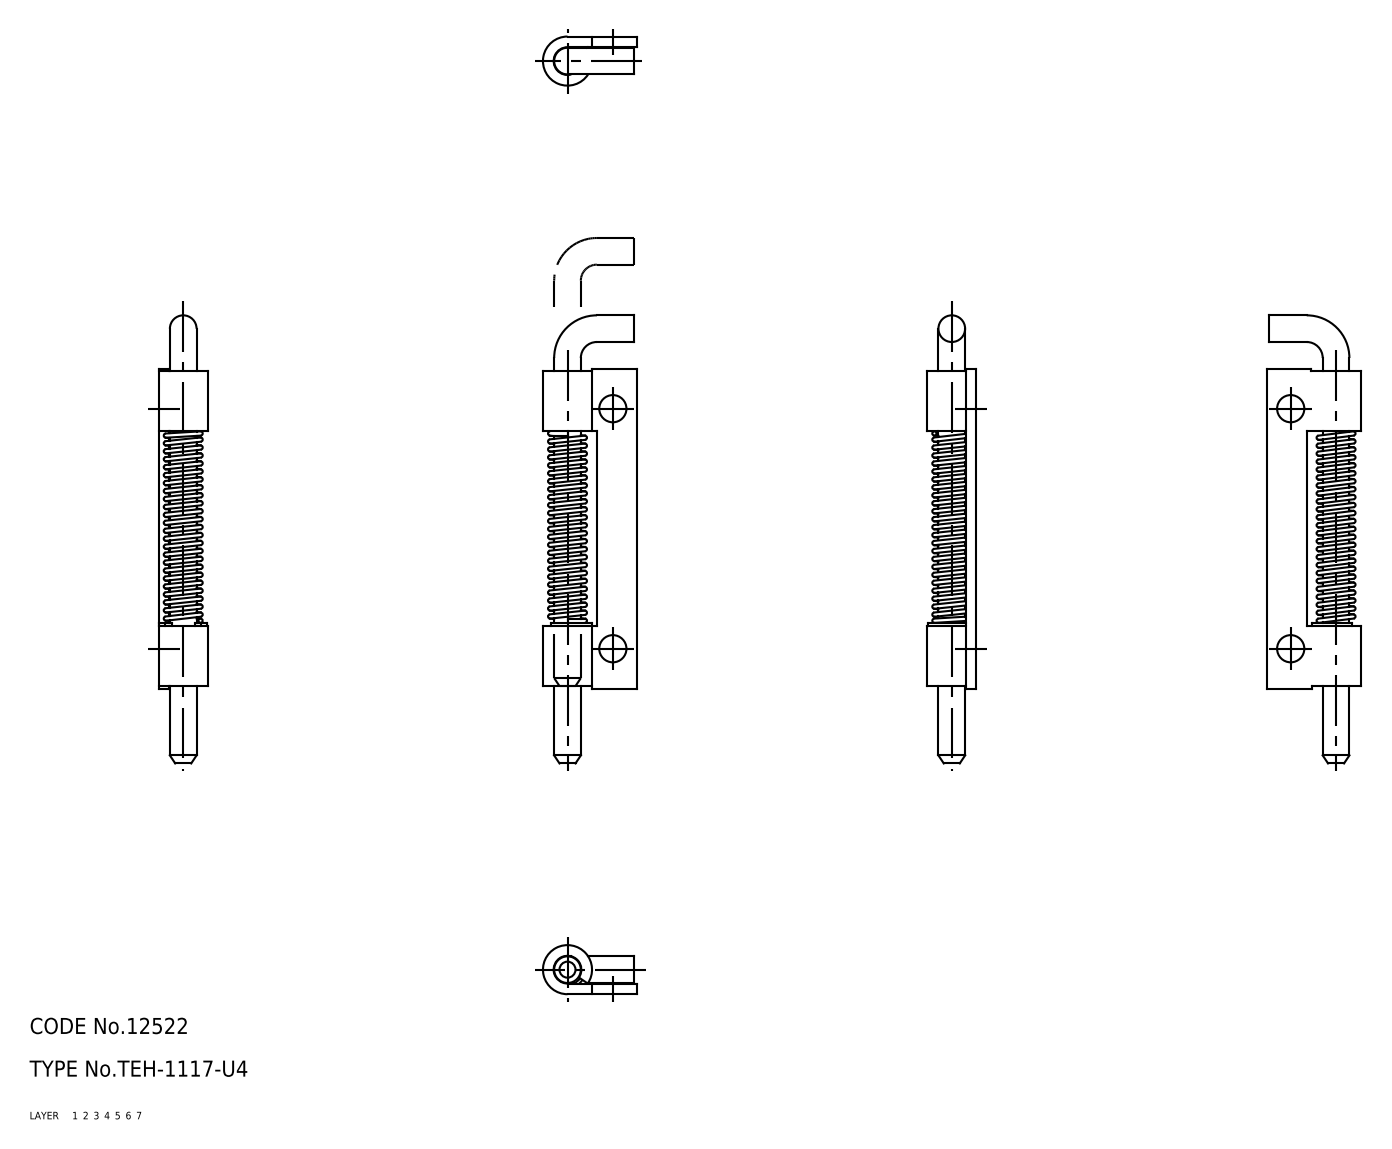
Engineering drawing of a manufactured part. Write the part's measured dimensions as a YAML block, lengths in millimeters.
part_name: "spring; shaft; retainer; hinge pieces (+1 more)"
step_written_by: "CADfix (AUTOMOTIVE_DESIGN)"
units: millimeters
bodies: {solids: 4, faces: 65, planar: 0, cylindrical: 0, other: 65}
overall_size: [84, 17.6, 9.2]
volume: 3980
surface_area: 5290
